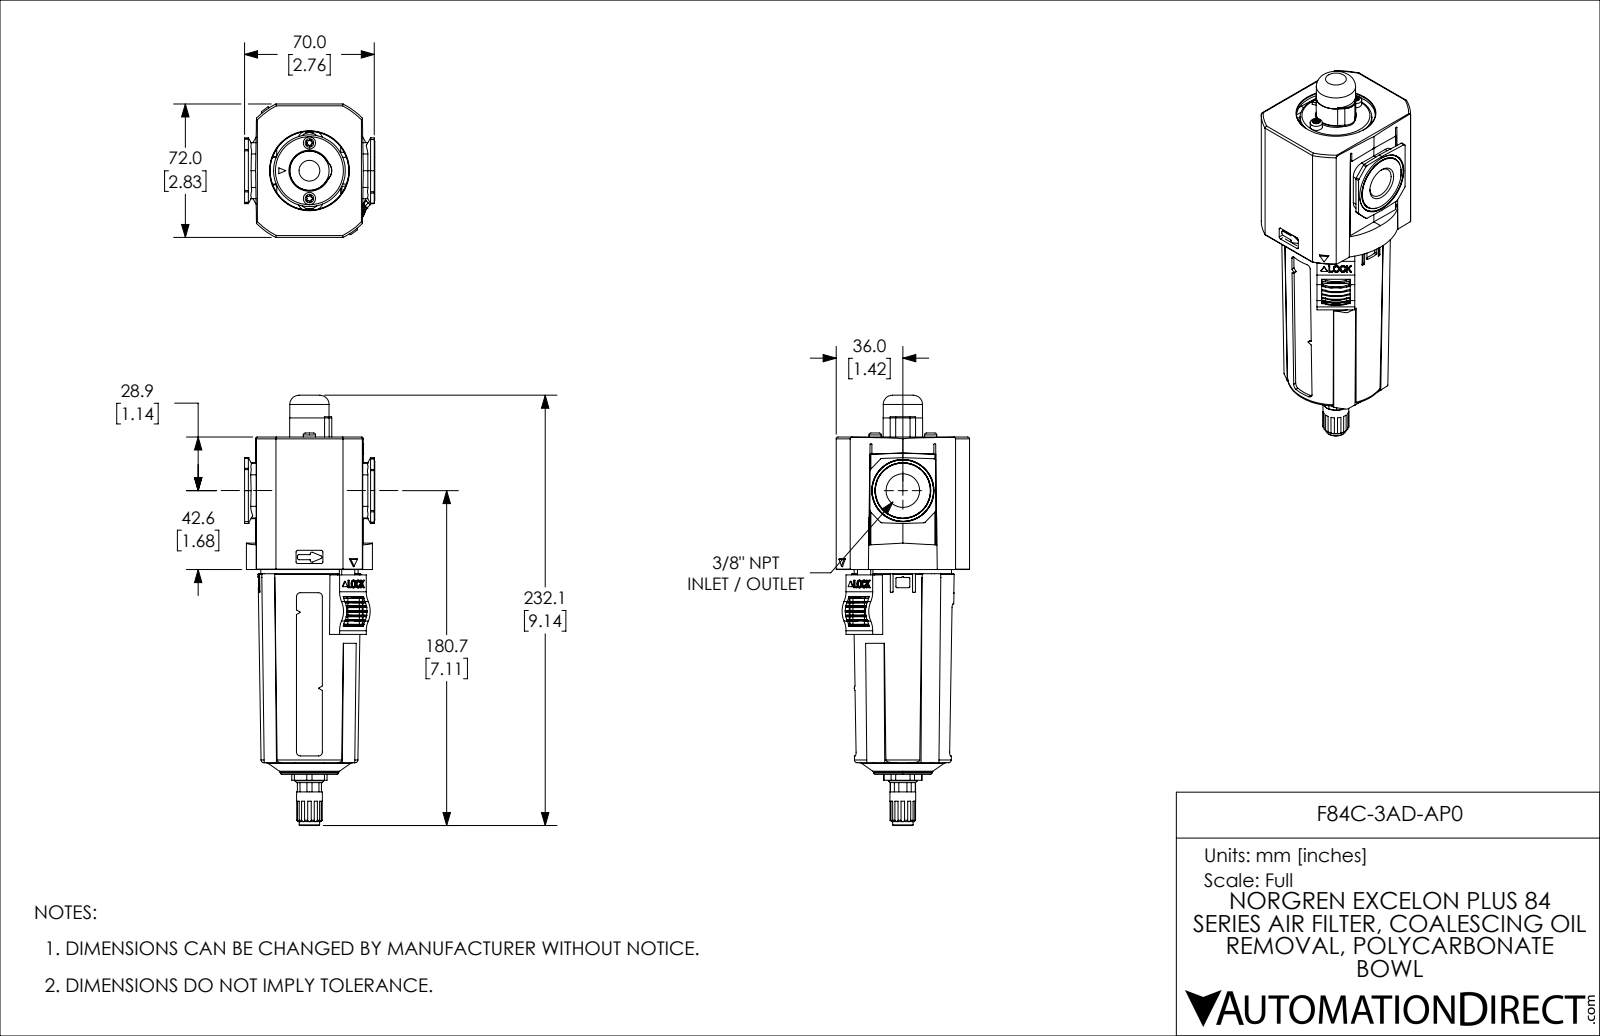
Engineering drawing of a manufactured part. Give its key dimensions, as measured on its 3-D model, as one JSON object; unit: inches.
{"part_name": "F84C-3AD-AP0", "step_written_by": "SolidWorks 2021 (CONFIG_CONTROL_DESIGN)", "units": "inches", "bodies": {"solids": 9, "faces": 1207, "planar": 546, "cylindrical": 467, "other": 194}, "overall_size": [9.139, 2.835, 2.766], "volume_in3": 29.21, "surface_area_in2": 156, "round_holes": [[0.163, 2], [0.177, 2], [0.22, 1], [0.246, 1], [0.776, 1], [0.969, 1], [2.461, 1]], "round_bosses_or_shafts": [[0.315, 2], [0.276, 2], [0.26, 2], [1.524, 1], [1, 1], [0.969, 1], [0.907, 1], [0.835, 1]], "partial_cylinders_radius": [[0.02, 60], [0.039, 44], [0.01, 24], [0.028, 16], [0.008, 10], [0.038, 8], [0.045, 8], [0.06, 8]], "face_to_face_distances": [2.835, 2.411, 0.059, 0.035, 2.376, 2.756, 1.951, 1.915, 0.461, 2.352], "hole_center_spacings": [0.591, 0.594, 1.185, 1.181, 1.189]}
